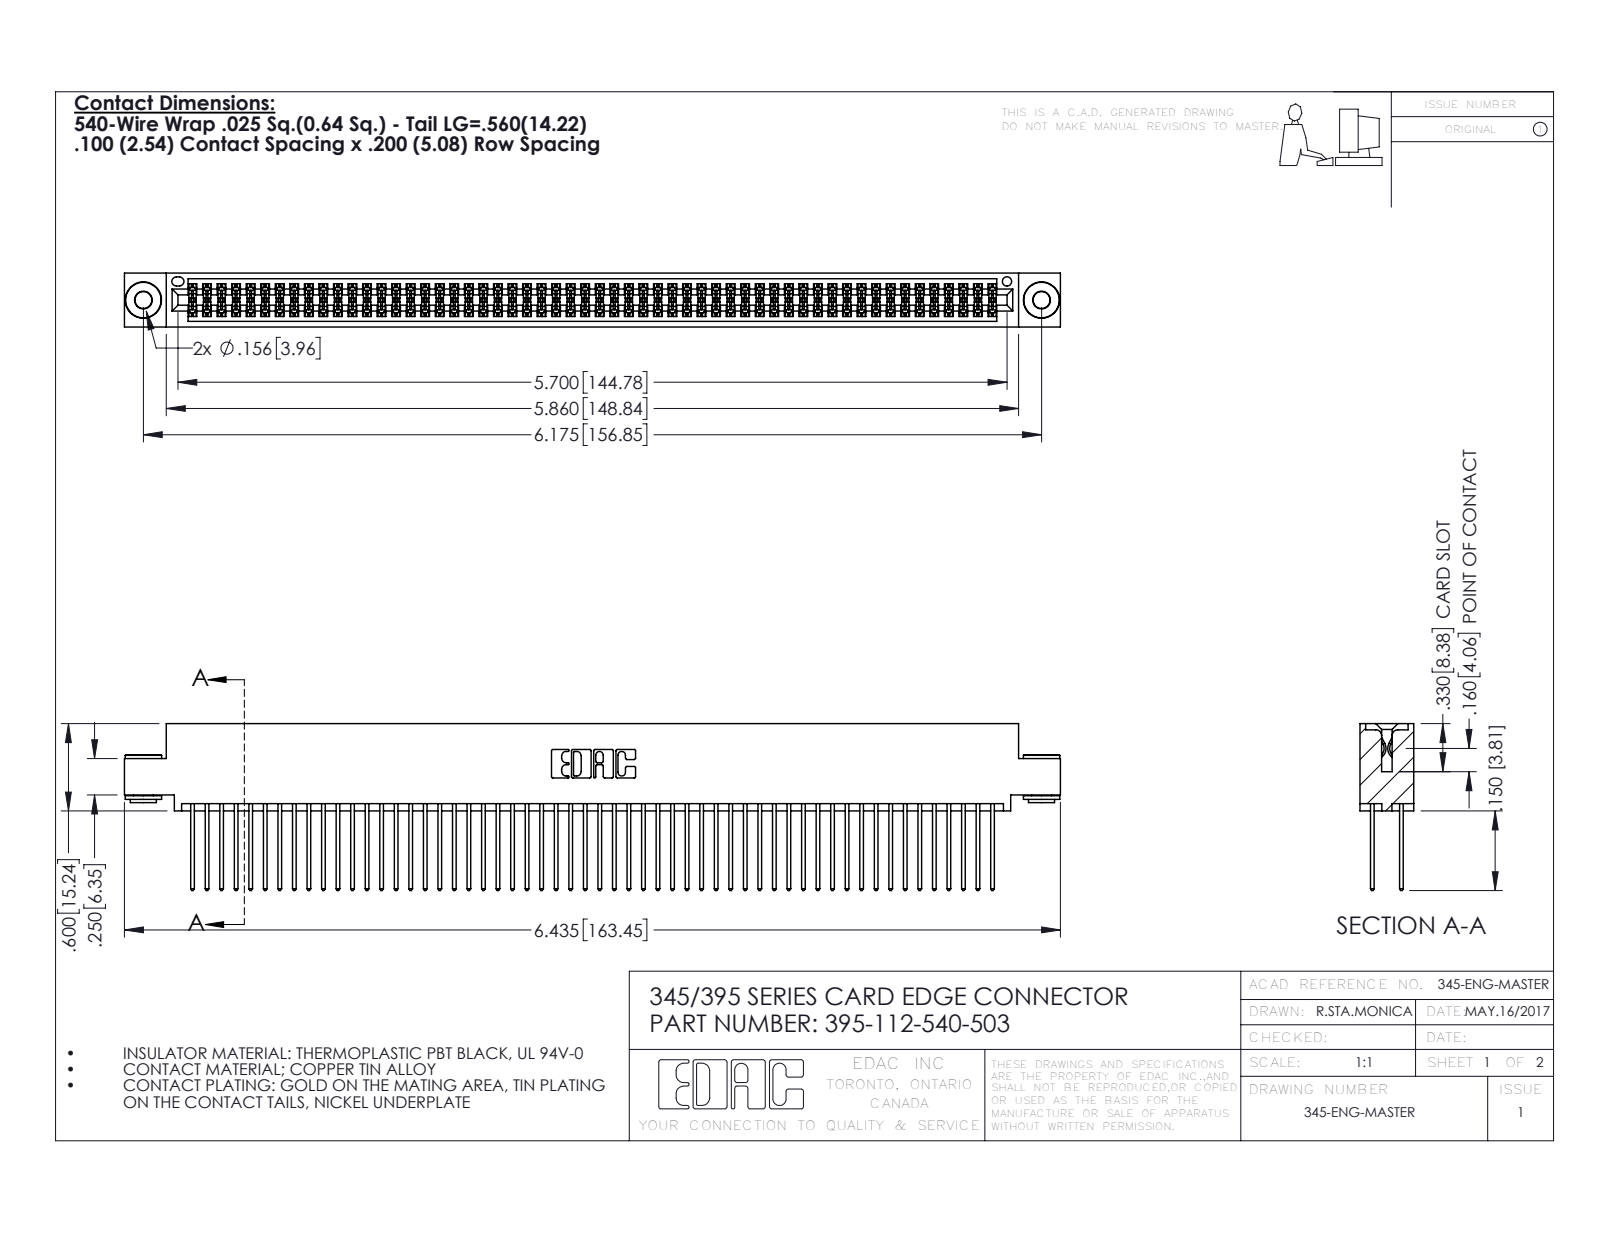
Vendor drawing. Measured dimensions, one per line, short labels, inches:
name: 345-250-002_345-250-002-102; 345-292-001_345-293-140; 345 Part_0.110 Offset - 0.156 Dia-TH; 395-112-540-503
written by: SolidWorks 2016 (CONFIG_CONTROL_DESIGN)
unit: in
bodies: 115 solids, 5768 faces (3790 planar, 1970 cylindrical, 8 other)
size: 6.435 × 1.147 × 0.37
volume: 0.999 in³; area: 41.46 in²
holes: 2× ⌀0.116, 2× ⌀0.156, 1× ⌀0.064
bosses: 2× ⌀0.25, 2× ⌀0.18, 2× ⌀0.136
rounds: 168× R0.006, 112× R0.01, 22× R0.01, 6× R0.007, 6× R0.031, 3× R0.026, 2× R0.014, 2× R0.019
face distances: 0.072, 0.298, 0.2, 0.025, 0.098, 0.272, 0.37, 0.225, 0.175, 0.149
hole spacings: 0.27, 5.939, 6.175
